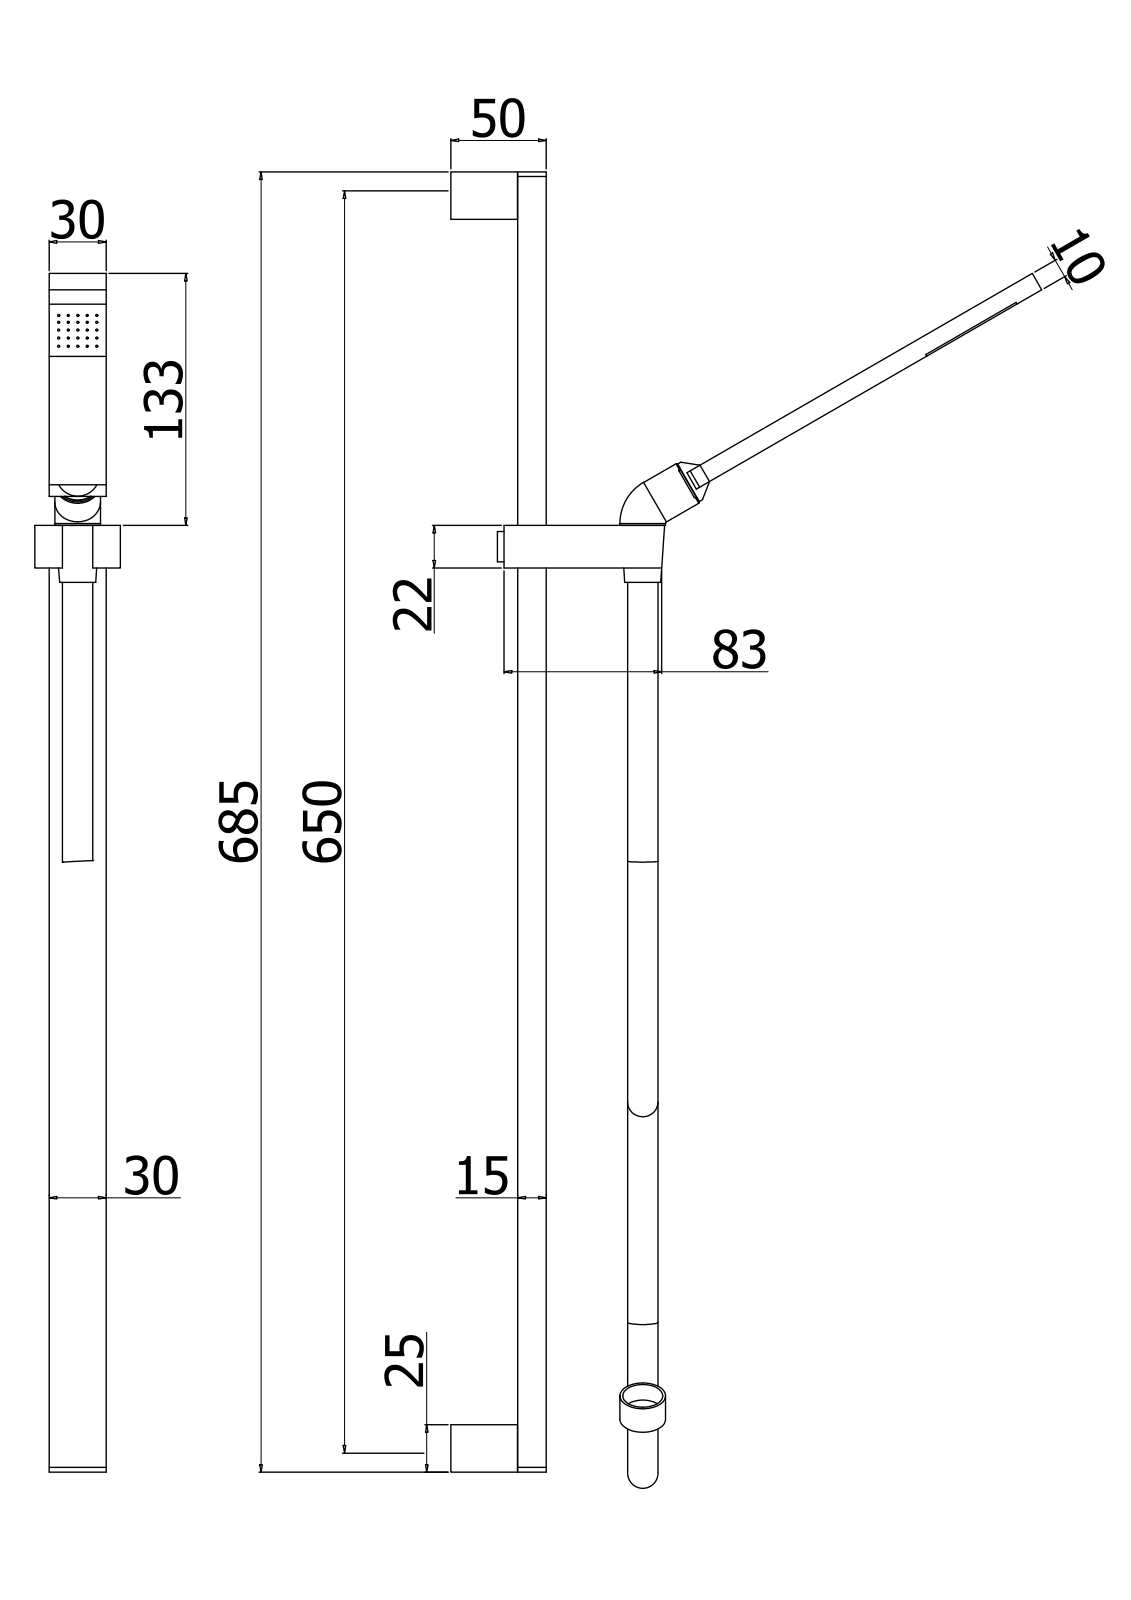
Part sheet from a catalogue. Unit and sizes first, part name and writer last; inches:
Units: inches
Overall size (bounding box): 26.929 × 12.257 × 5.512
Round holes (diameter × count): ⌀0.15 ×1, ⌀0.189 ×1, ⌀0.276 ×1, ⌀0.394 ×1, ⌀0.472 ×1
Round bosses / shafts (diameter × count): ⌀0.079 ×11, ⌀0.886 ×1, ⌀0.457 ×1, ⌀0.307 ×1, ⌀0.268 ×1
Partial cylindrical surfaces — rounded edges, fillets, slot ends (radius × count): R0.02 ×75, R0.039 ×30, R0.008 ×16, R0.012 ×12, R0.079 ×10, R0.016 ×4, R0.069 ×4, R0.102 ×4
Main face-to-face distances: 0.031, 0.559, 0.591, 0.528, 1.15, 1.181, 0.079, 1.118, 0.047, 0.039
Volume: 15.45 in³ · Surface area: 381.1 in²
Bodies: 3 solids, 1321 faces (709 planar, 315 cylindrical, 297 other)
Part name (STEP PRODUCT): ZSAL079CR
STEP written by: CREO PARAMETRIC BY PTC INC, 2020044 (CONFIG_CONTROL_DESIGN)
